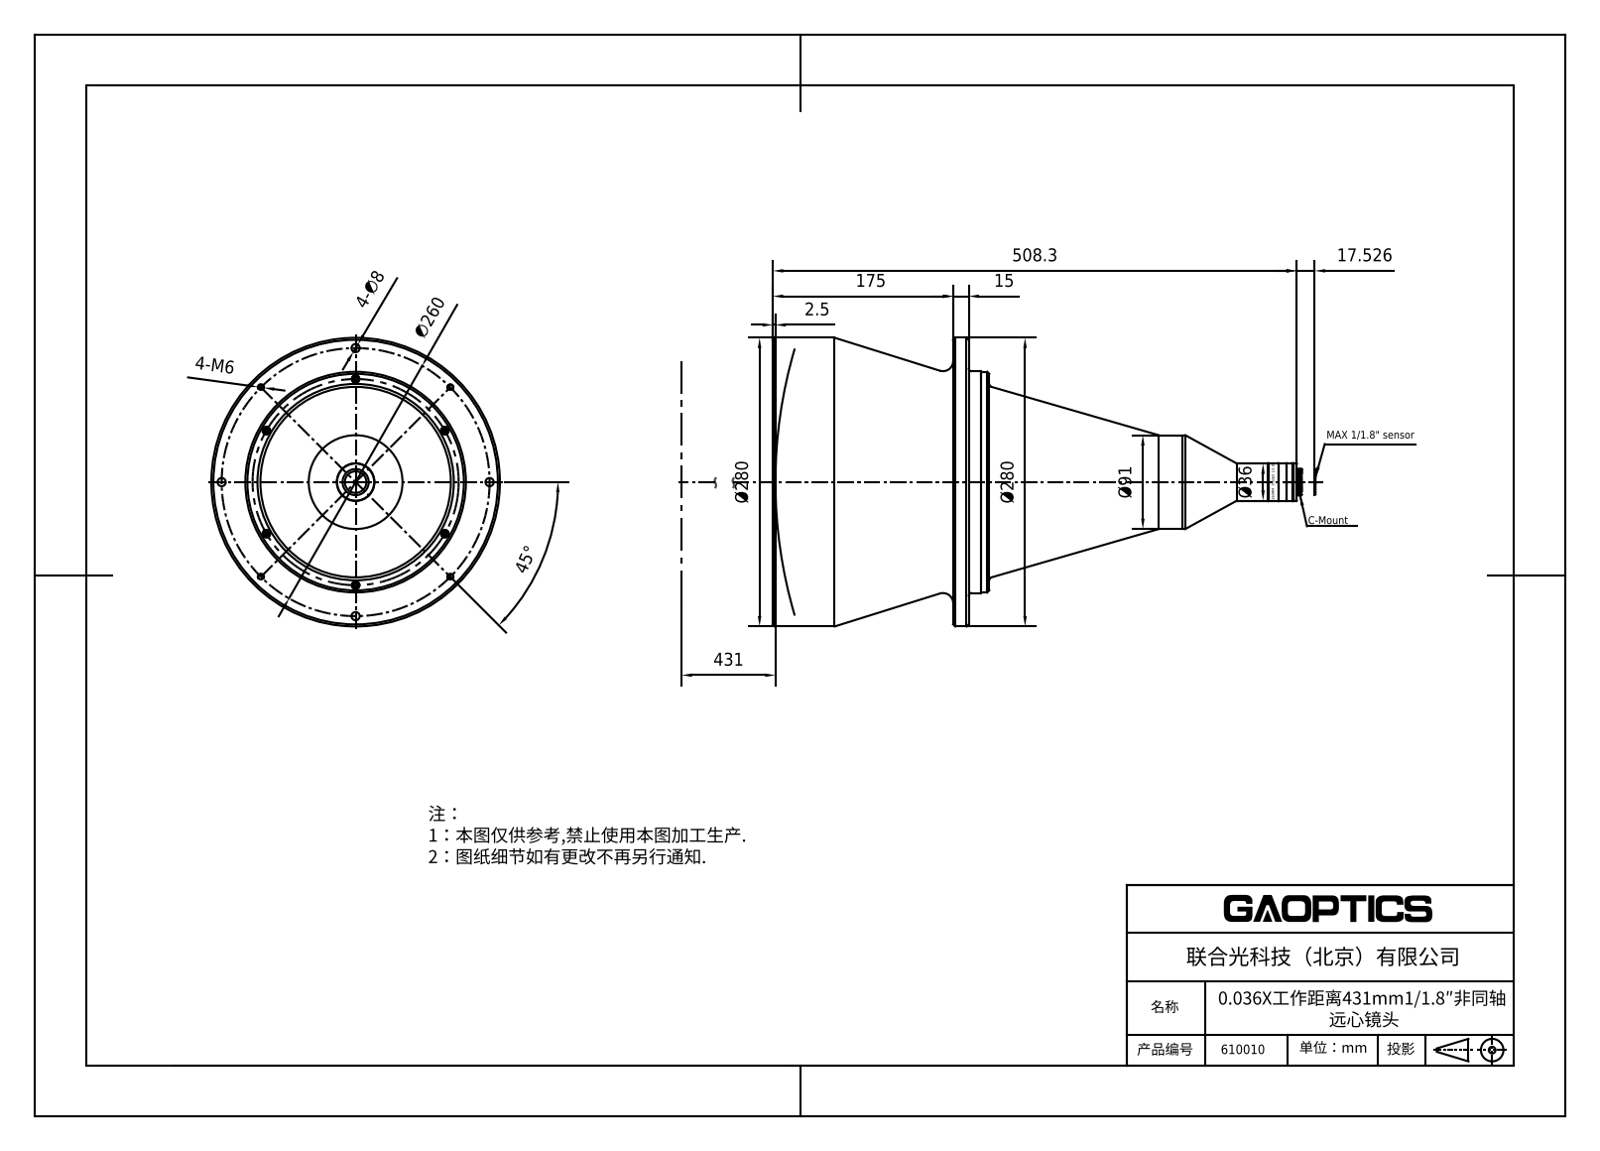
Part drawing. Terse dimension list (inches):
name: 610010
written by: SolidWorks 2020 (CONFIG_CONTROL_DESIGN)
unit: in
bodies: 0 solids, 864 faces (314 planar, 113 cylindrical, 437 other)
size: 20.224 × 11.024 × 11.024
holes: 6× ⌀0.276, 1× ⌀0.803, 1× ⌀1.244, 1× ⌀1.394, 1× ⌀1.417, 1× ⌀1.441, 1× ⌀3.583, 1× ⌀8.425, 1× ⌀8.465, 1× ⌀11.024
bosses: 6× ⌀0.295, 4× ⌀0.315, 4× ⌀0.197, 1× ⌀10.465, 1× ⌀10.087, 1× ⌀1
rounds: 1× R0.713, 1× R0.717, 1× R0.719
face distances: 6.632, 0.591, 6.042, 7.42, 1.378, 0.787, 13.886, 7.844, 7.254, 6.466
hole spacings: 3.937, 6.819, 7.874
